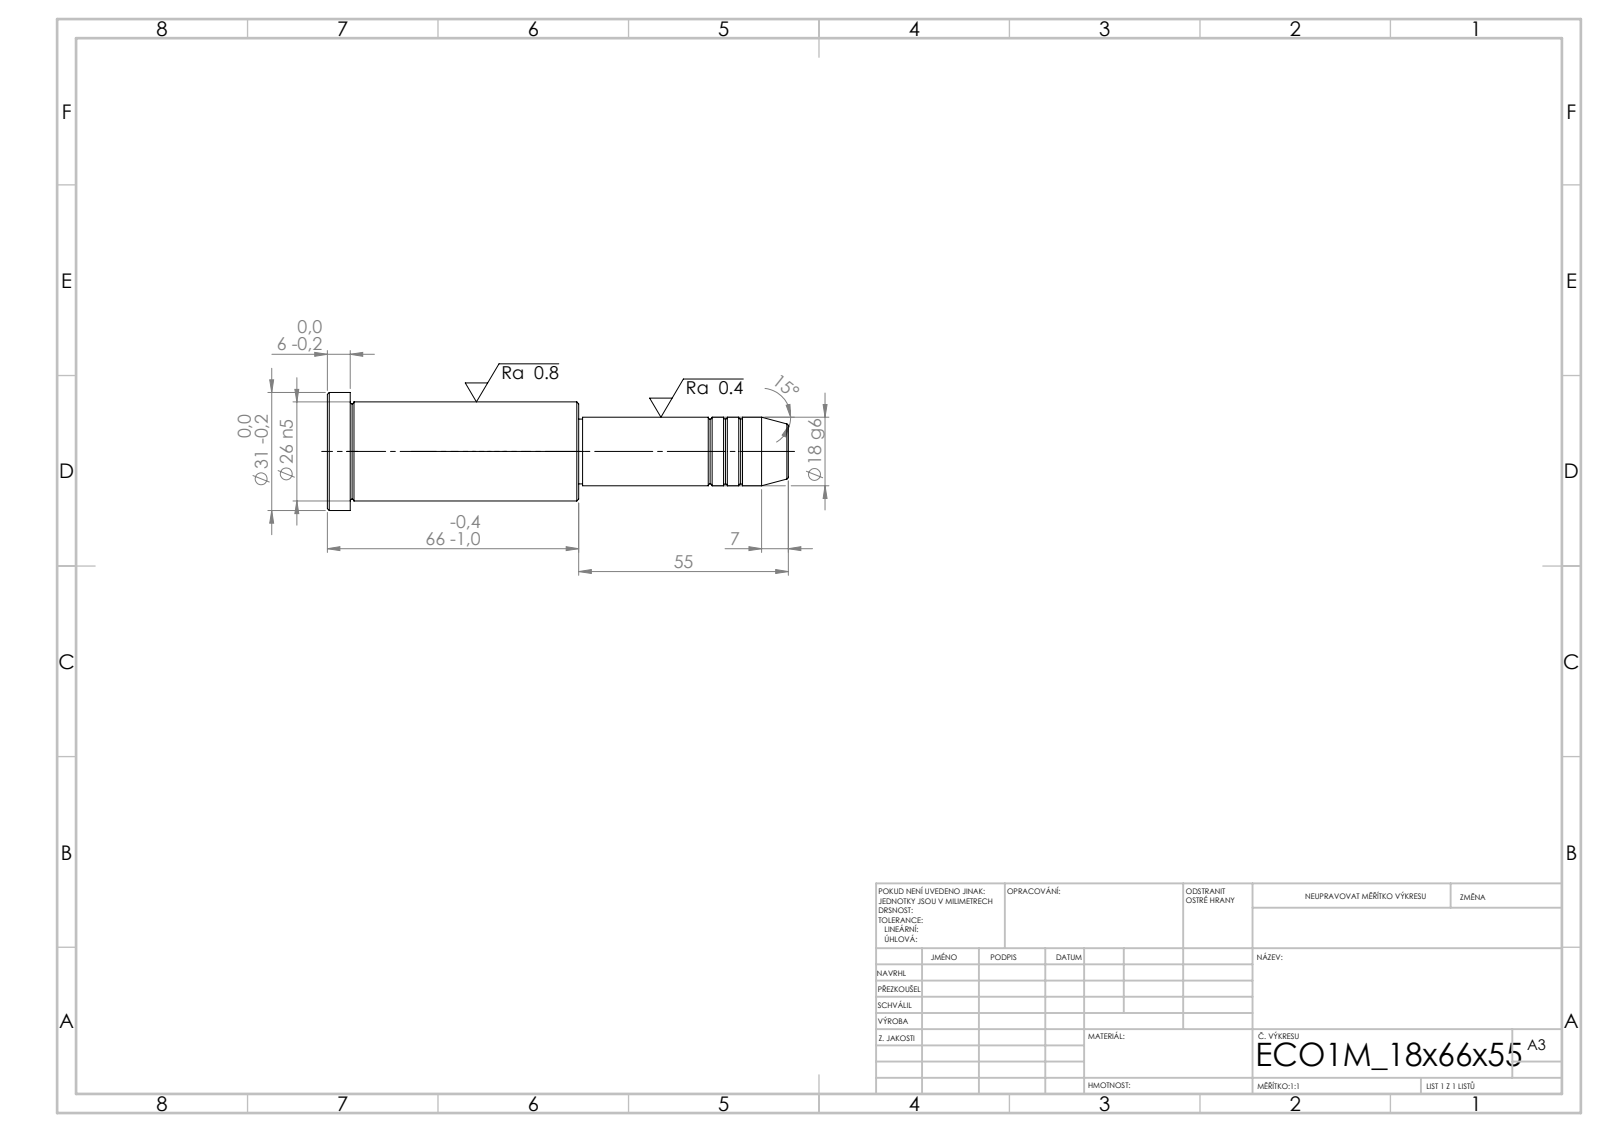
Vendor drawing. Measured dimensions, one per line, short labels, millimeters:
written by: SolidWorks 2019 (CONFIG_CONTROL_DESIGN)
unit: mm
bodies: 1 solid, 43 faces (5 planar, 14 cylindrical, 24 other)
size: 121 × 31 × 31
volume: 49 887 mm³; area: 10 106 mm²
bosses: 1× ⌀31, 1× ⌀26, 1× ⌀18, 1× ⌀17
face distances: 66, 60, 6, 55, 115, 121, 54, 1, 61, 67
